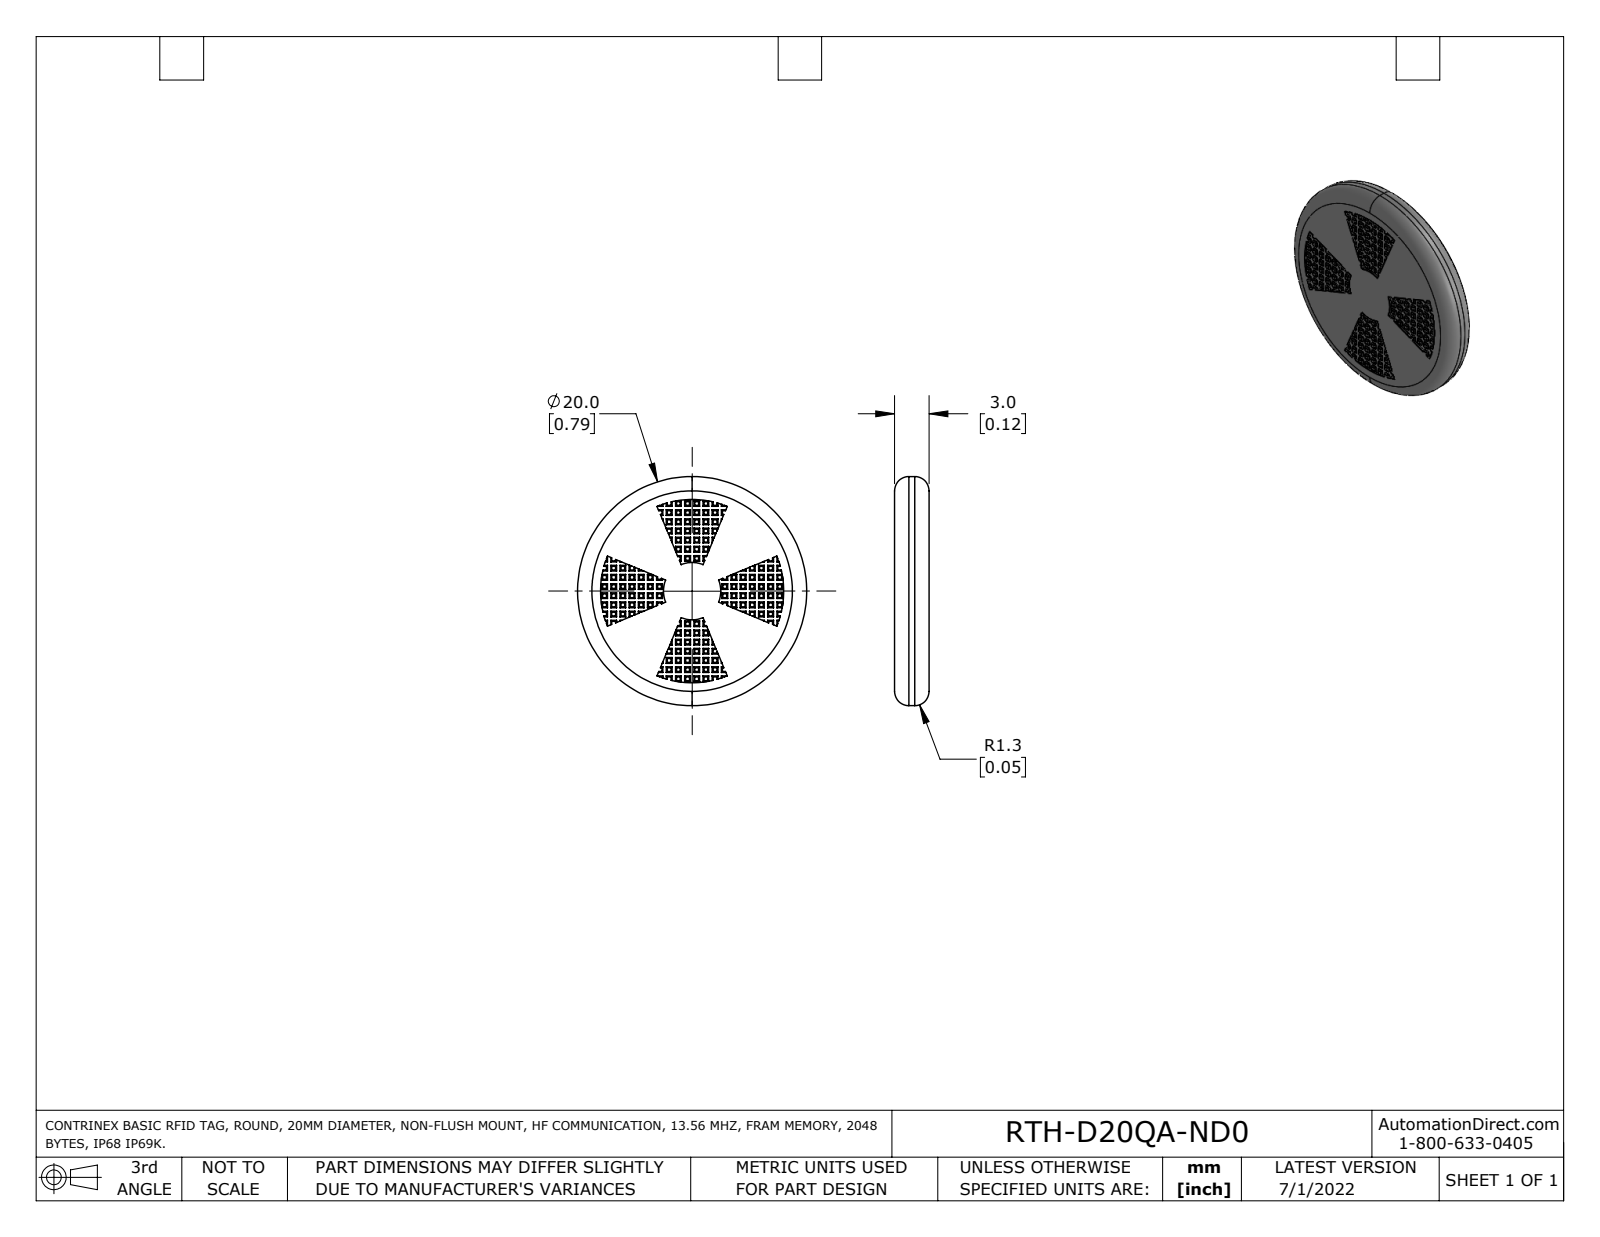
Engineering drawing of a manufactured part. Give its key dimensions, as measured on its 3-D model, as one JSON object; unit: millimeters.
{"part_name": "RTH-D20QA-ND0", "step_written_by": "SolidWorks 2021 (AUTOMOTIVE_DESIGN)", "units": "millimeters", "bodies": {"solids": 1, "faces": 830, "planar": 798, "cylindrical": 28, "other": 4}, "overall_size": [20, 20, 3], "volume_mm3": 892, "surface_area_mm2": 777, "round_bosses_or_shafts": [[20, 1]], "partial_cylinders_radius": [[2.5, 1], [8, 1]], "face_to_face_distances": [3, 2.85, 0.69, 4.2, 4.89, 2.08, 1.39, 1.38, 6.97, 6.28]}
